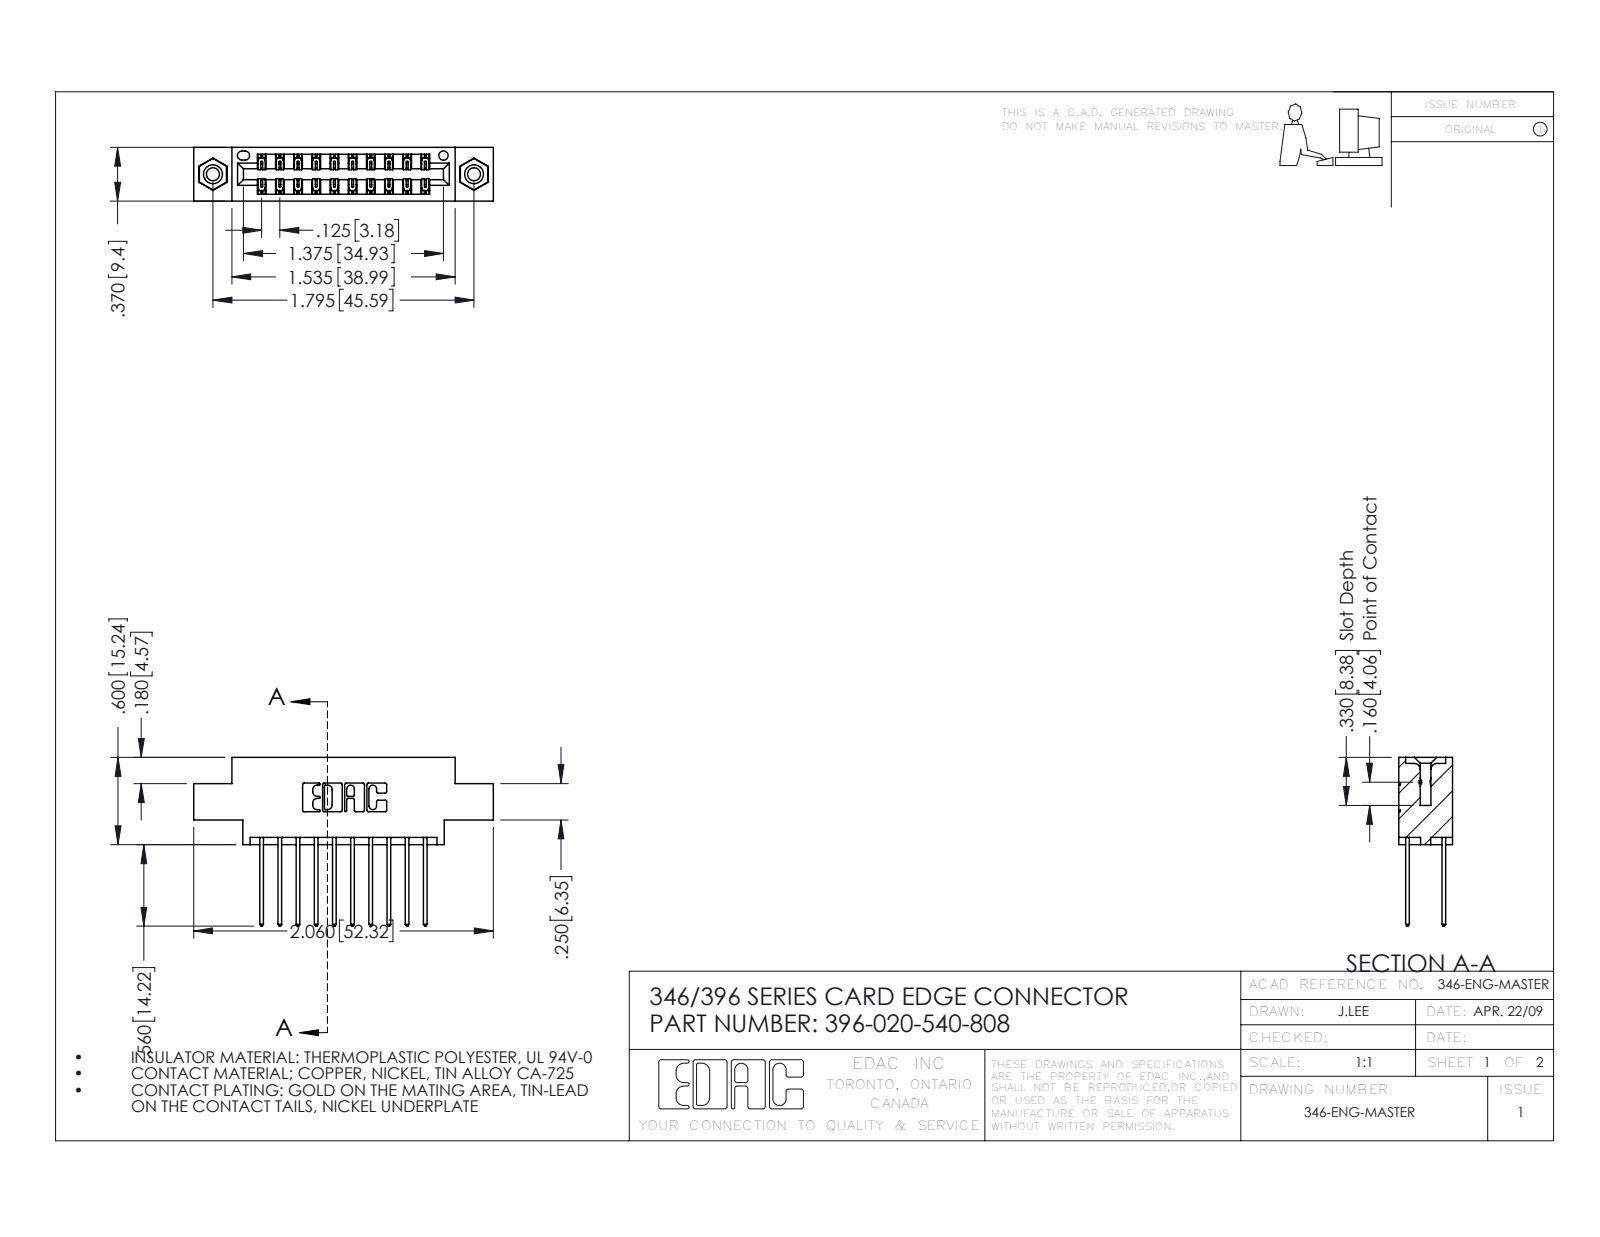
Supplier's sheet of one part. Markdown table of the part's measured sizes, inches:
| quantity | value |
| --- | --- |
| part name | 345-250-001_345-250-003-102; 345-292-001_345-293-140; 396-020-540-808; 346 Part_0.170 Offset - 0.156 Dia-TI |
| STEP written by | SolidWorks 2016 (CONFIG_CONTROL_DESIGN) |
| units | inches |
| bodies | 23 solids, 1226 faces (812 planar, 398 cylindrical, 16 other) |
| overall size | 2.06 × 1.16 × 0.37 |
| volume | 0.291 in³ |
| surface area | 10.25 in² |
| round holes (diameter × count) | 0.089 × 2, 0.125 × 2, 0.156 × 2, 0.064 × 1 |
| round bosses / shafts (diameter × count) | 0.155 × 2 |
| partial cylindrical surfaces (radius × count) | 0.006 × 30, 0.01 × 22, 0.01 × 20, 0.007 × 6, 0.031 × 6, 0.026 × 3, 0.014 × 2, 0.022 × 2 |
| main face-to-face distances | 0.25, 0.048, 0.322, 0.37, 0.072, 0.298, 0.025, 0.275, 0.222, 0.148 |
| hole center spacings | 0.246, 1.59, 1.795 |
